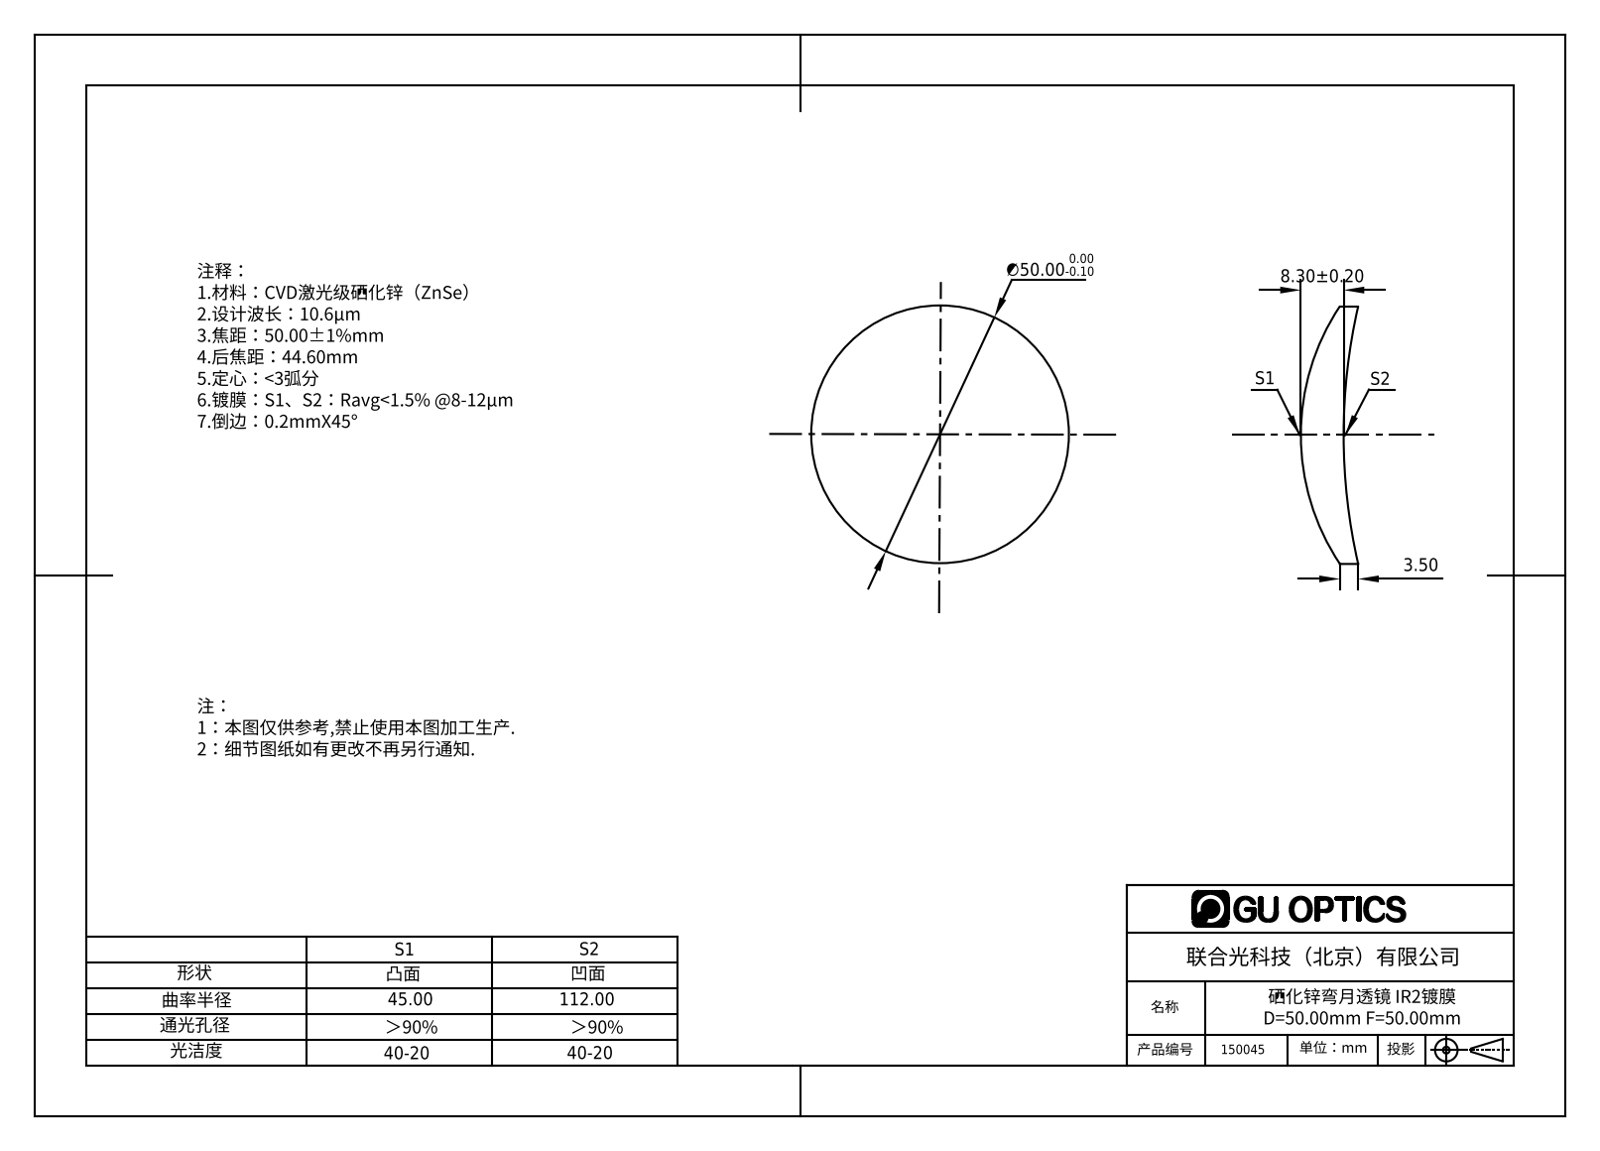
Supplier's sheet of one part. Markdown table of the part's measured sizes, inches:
| quantity | value |
| --- | --- |
| part name | 150020 |
| STEP written by | SolidWorks 2016 (AUTOMOTIVE_DESIGN) |
| units | inches |
| bodies | 1 solid, 6 faces (0 planar, 2 cylindrical, 4 other) |
| overall size | 1.969 × 1.969 × 0.438 |
| volume | 0.723 in³ |
| surface area | 7.268 in² |
| round bosses / shafts (diameter × count) | 1.969 × 1 |
